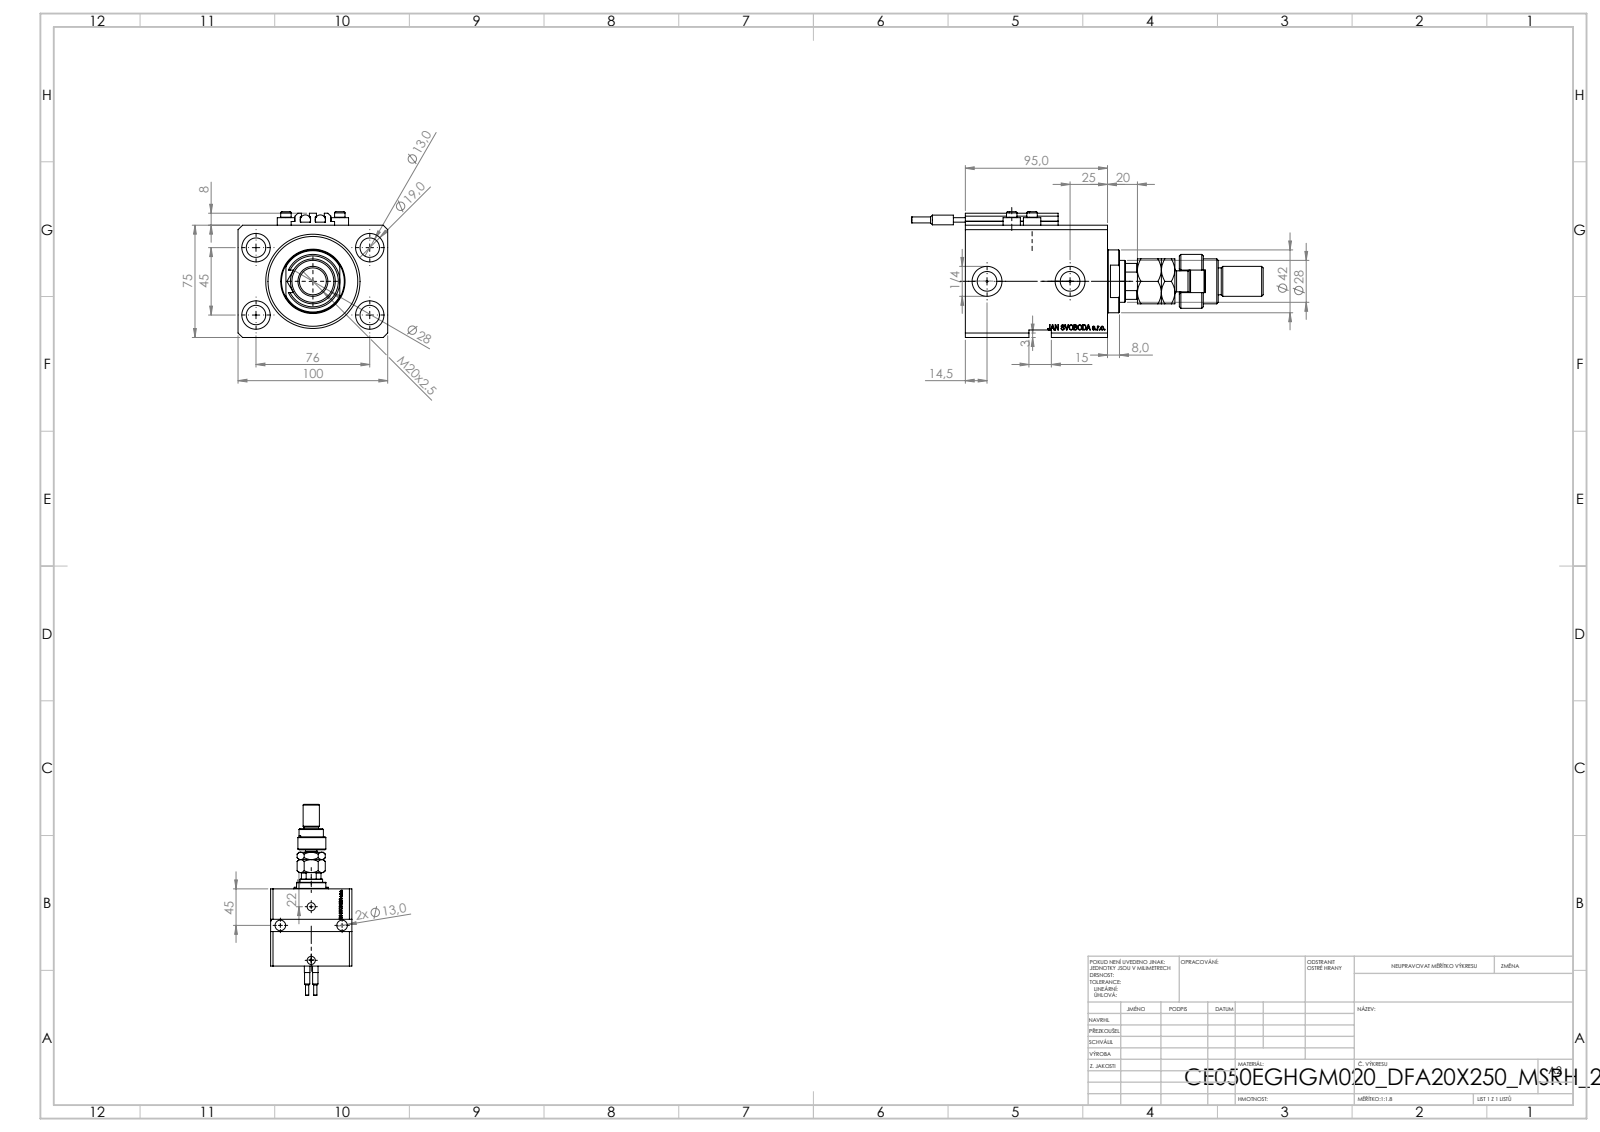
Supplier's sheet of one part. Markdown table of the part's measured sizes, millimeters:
| quantity | value |
| --- | --- |
| part name | V250CE_VC_E; FEMALE_PART_FOR_DFA; ALLEN BOLT V250CE; V250CE_C_VCP (+3 more) |
| STEP written by | SolidWorks 2019 (CONFIG_CONTROL_DESIGN) |
| units | millimeters |
| bodies | 12 solids, 1225 faces (595 planar, 151 cylindrical, 479 other) |
| overall size | 235 × 100 × 84 |
| volume | 663 469 mm³ |
| surface area | 137 886 mm² |
| round holes (diameter × count) | 13 × 6, 1.25 × 4, 4 × 4, 19 × 4, 10 × 2, 13.16 × 2, 20 × 2, 18.5 × 1, 28 × 1, 50 × 1, 63 × 1 |
| round bosses / shafts (diameter × count) | 11.6 × 4, 7 × 4, 6.8 × 2, 6.5 × 2, 4 × 2, 42 × 1, 36 × 1, 30 × 1 |
| partial cylindrical surfaces (radius × count) | 0.2 × 10, 7.5 × 1, 12 × 1, 13.5 × 1 |
| main face-to-face distances | 75, 20, 100, 95, 11.9, 83.1, 63.1, 40, 5, 3 |
| hole center spacings | 44.16, 76, 13.6, 20.72, 27.59, 29.58, 30, 33.62 |
